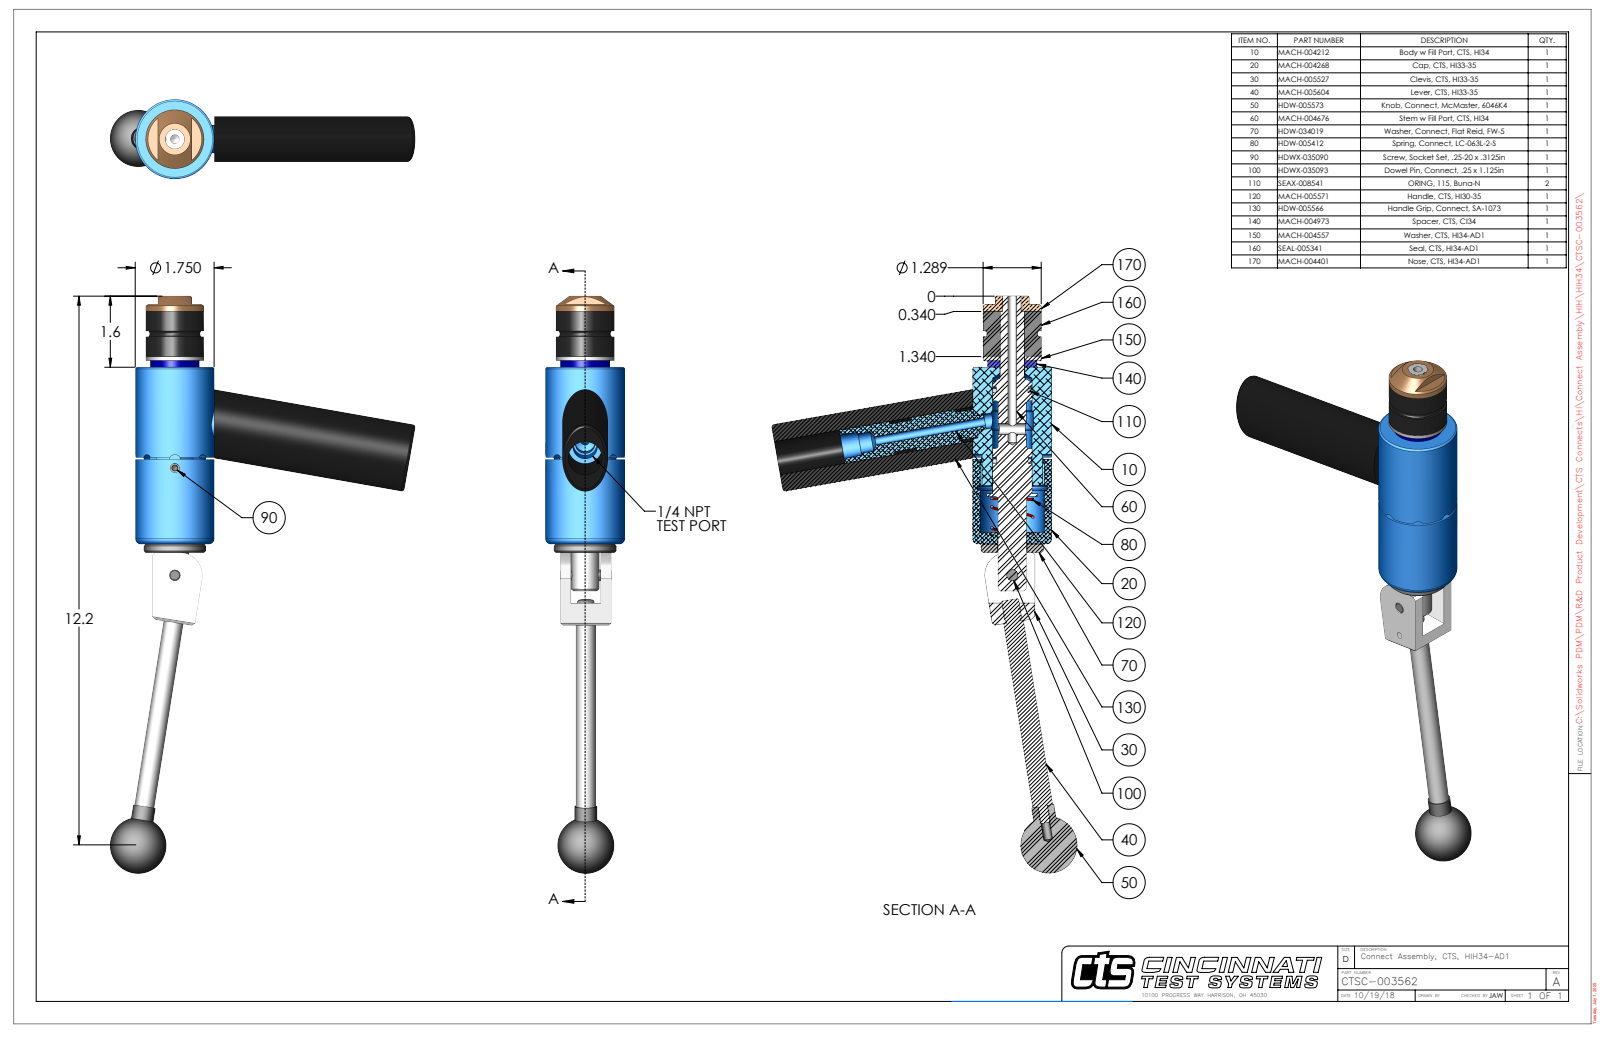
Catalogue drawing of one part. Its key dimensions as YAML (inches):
part_name: "CTSC-003562"
step_written_by: "SolidWorks 2023 (AUTOMOTIVE_DESIGN)"
units: inches
bodies: {solids: 11, faces: 302, planar: 109, cylindrical: 124, other: 69}
overall_size: [12.795, 6.763, 1.75]
volume: 18.6
surface_area: 118.4
round_holes:
  - {diameter: 0.201, count: 2}
  - {diameter: 0.15, count: 1}
  - {diameter: 0.187, count: 1}
  - {diameter: 0.204, count: 1}
  - {diameter: 0.249, count: 1}
  - {diameter: 0.25, count: 1}
  - {diameter: 0.251, count: 1}
  - {diameter: 0.313, count: 1}
  - {diameter: 0.422, count: 1}
  - {diameter: 0.438, count: 1}
  - {diameter: 0.53, count: 1}
  - {diameter: 0.541, count: 1}
round_bosses_or_shafts:
  - {diameter: 0.5, count: 2}
  - {diameter: 0.44, count: 2}
  - {diameter: 0.25, count: 2}
  - {diameter: 1.75, count: 1}
  - {diameter: 1.38, count: 1}
  - {diameter: 1.289, count: 1}
  - {diameter: 1.09, count: 1}
  - {diameter: 0.75, count: 1}
partial_cylinders:
  - {radius: 0.125, count: 4}
  - {radius: 0.029, count: 2}
  - {radius: 0.185, count: 1}
  - {radius: 0.33, count: 1}
  - {radius: 0.5, count: 1}
  - {radius: 0.695, count: 1}
  - {radius: 0.836, count: 1}
face_to_face_distances: [3.921, 1.237, 5.158, 1, 0.237, 4.158, 1.094, 0.094, 0.143, 4.064]
hole_center_spacings: [0.74, 2.376, 3.116]
